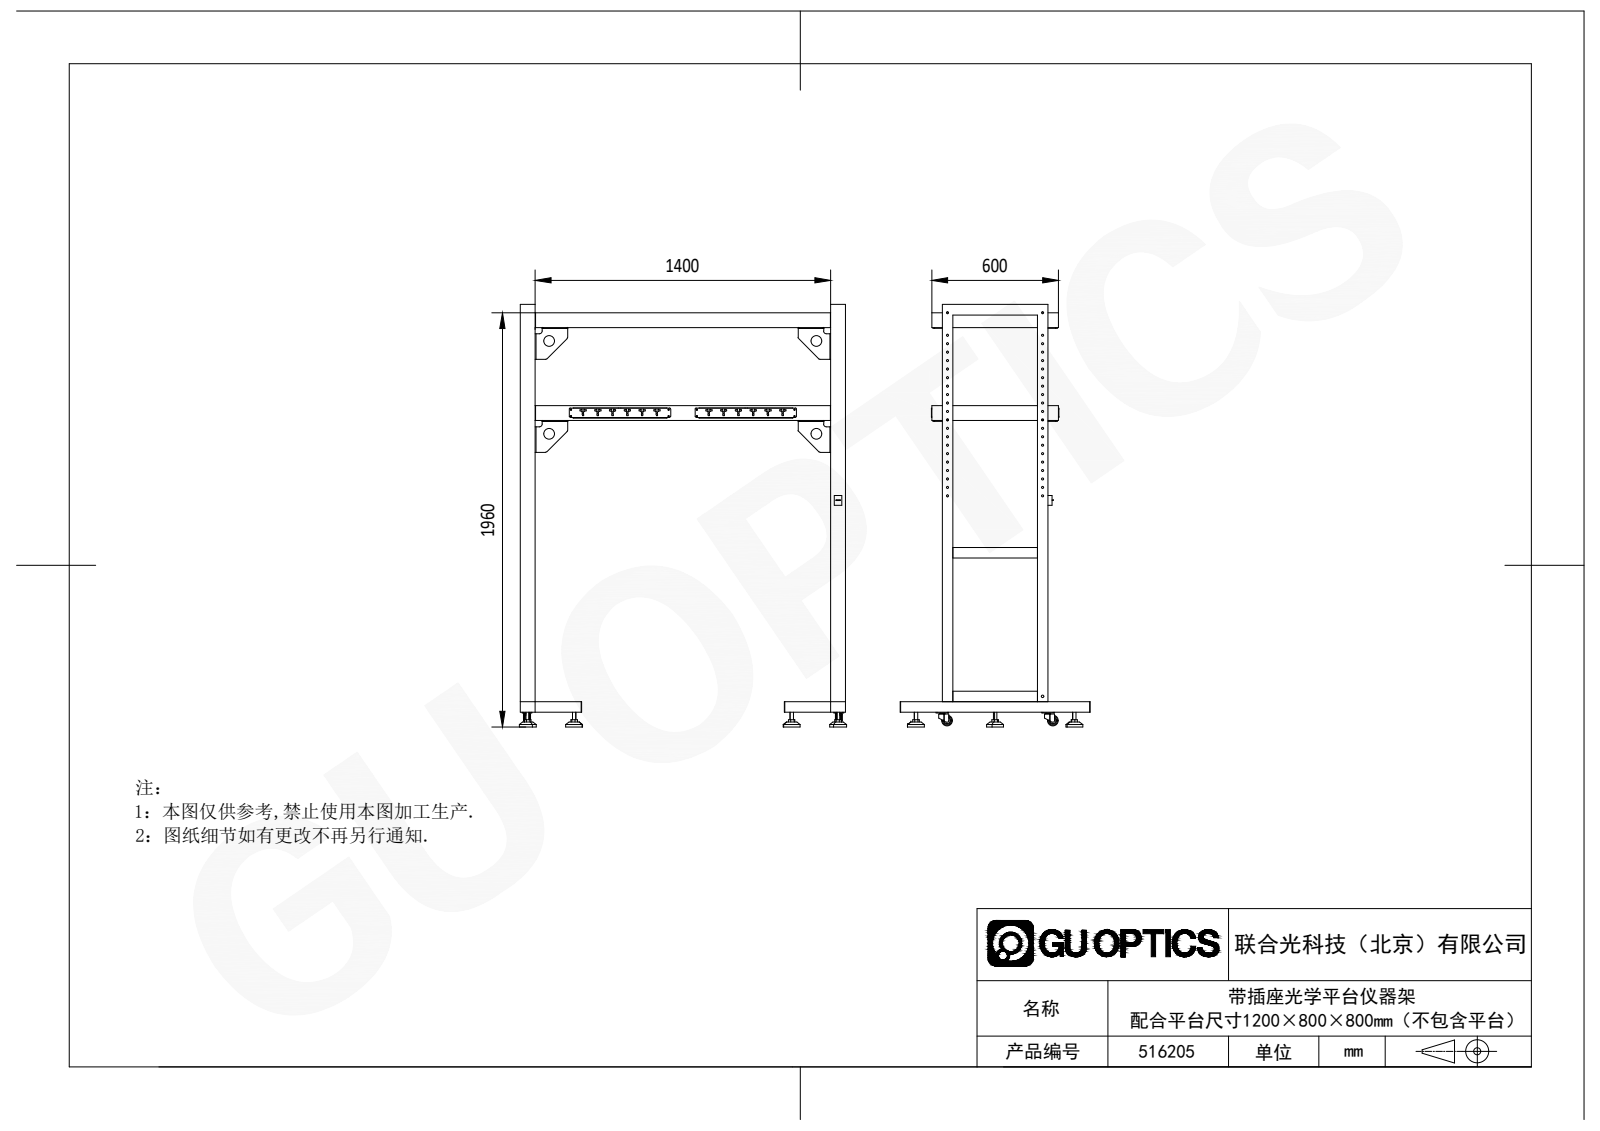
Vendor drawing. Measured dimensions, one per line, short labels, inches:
name: 516205
written by: SolidWorks 2020 (CONFIG_CONTROL_DESIGN)
unit: in
bodies: 59 solids, 2531 faces (1423 planar, 1048 cylindrical, 60 other)
size: 78.78 × 61.024 × 35.433
volume: 1 216 in³; area: 20 660 in²
holes: 66× ⌀0.354, 16× ⌀0.24, 16× ⌀0.394, 12× ⌀0.256, 8× ⌀0.165, 8× ⌀0.205, 8× ⌀0.236, 6× ⌀0.669, 6× ⌀0.709, 6× ⌀1.024, 6× ⌀2.717, 4× ⌀0.126
bosses: 6× ⌀3.15, 6× ⌀0.63, 4× ⌀1.024, 4× ⌀0.709, 2× ⌀1.969, 2× ⌀0.394
rounds: 36× R0.197, 24× R0.276, 16× R0.118, 12× R0.167, 8× R0.059, 8× R0.158, 4× R0.059, 4× R0.512
face distances: 17.323, 0.079, 0.118, 2.756, 0.059, 1.969, 2.638, 17.717, 57.874, 1.89
hole spacings: 1.575, 3.15, 4.724, 11.024, 6.299, 7.874, 9.449, 12.598
